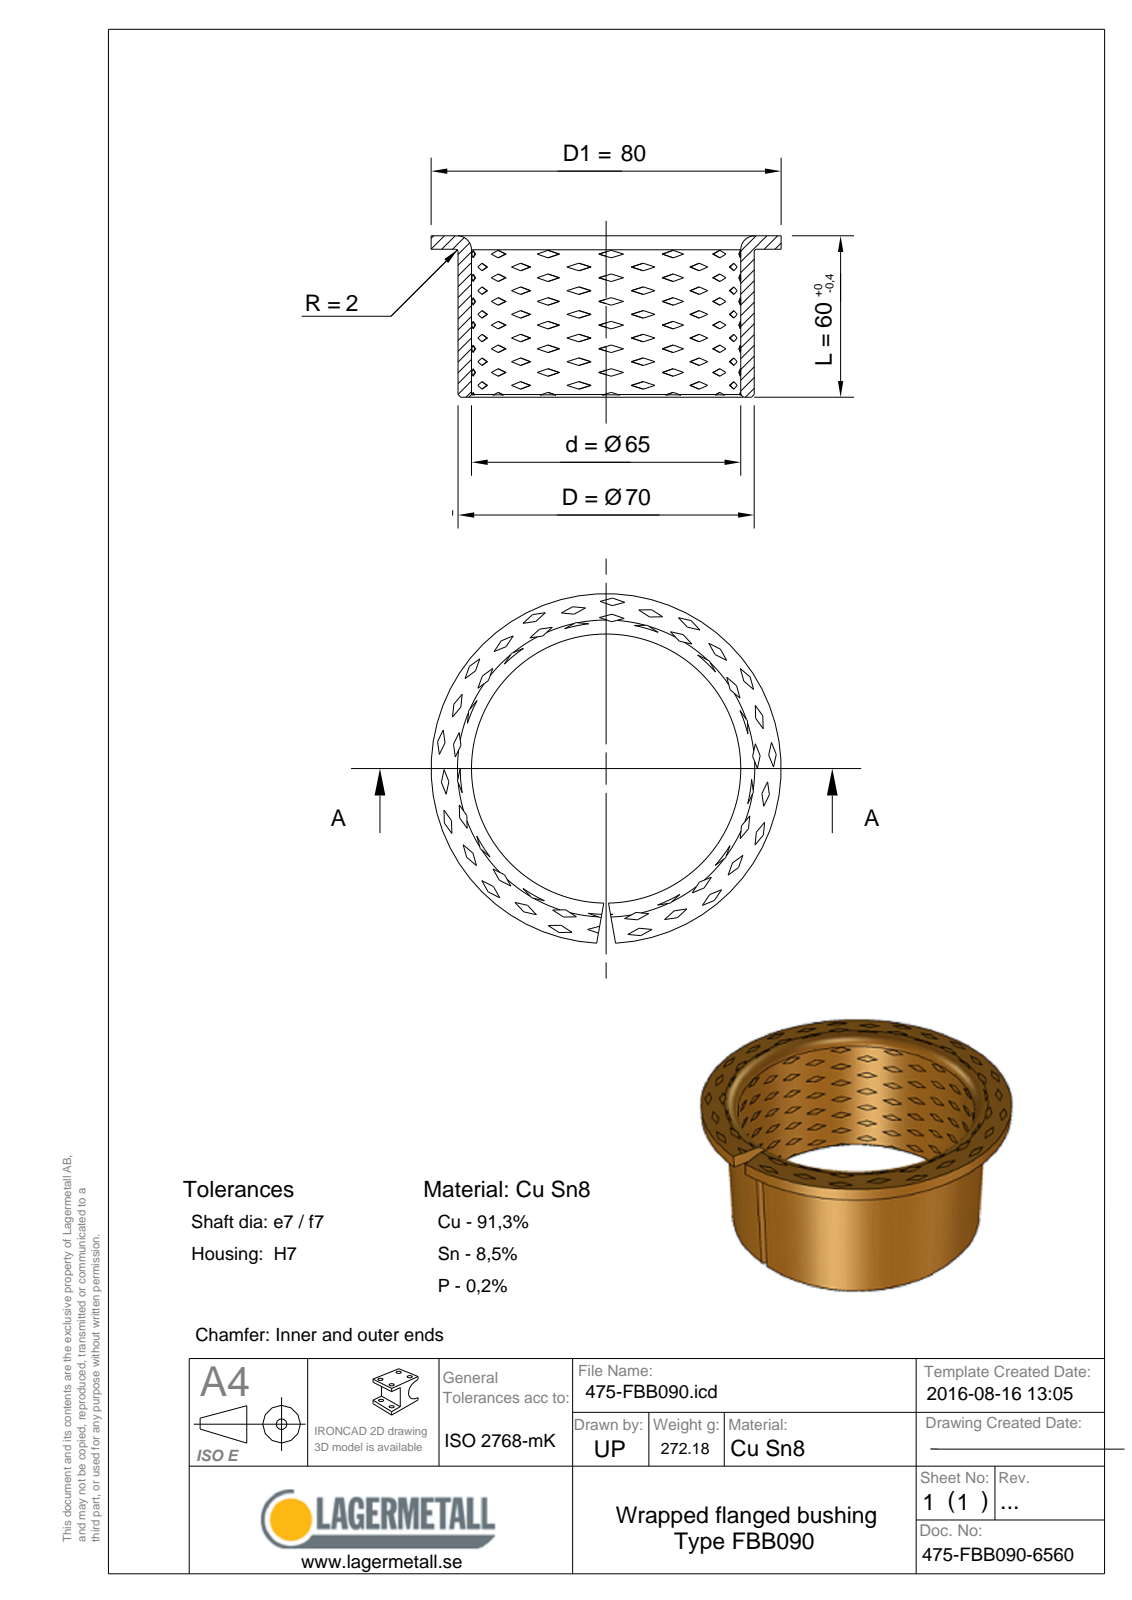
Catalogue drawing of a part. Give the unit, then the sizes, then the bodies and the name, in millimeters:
Units: millimetres
Overall size (bounding box): 80 × 79.96 × 60
Round holes (diameter × count): ⌀65 ×1
Round bosses / shafts (diameter × count): ⌀80 ×1, ⌀70 ×1
Main face-to-face distances: 2.5, 57.5, 60
Volume: 33 603 mm³ · Surface area: 28 280 mm²
Bodies: 1 solid, 12 faces (5 planar, 3 cylindrical, 4 other)
Part name (STEP PRODUCT): 475-FBB090-6560
STEP written by: Spatial InterOp 3D (CONFIG_CONTROL_DESIGN)
